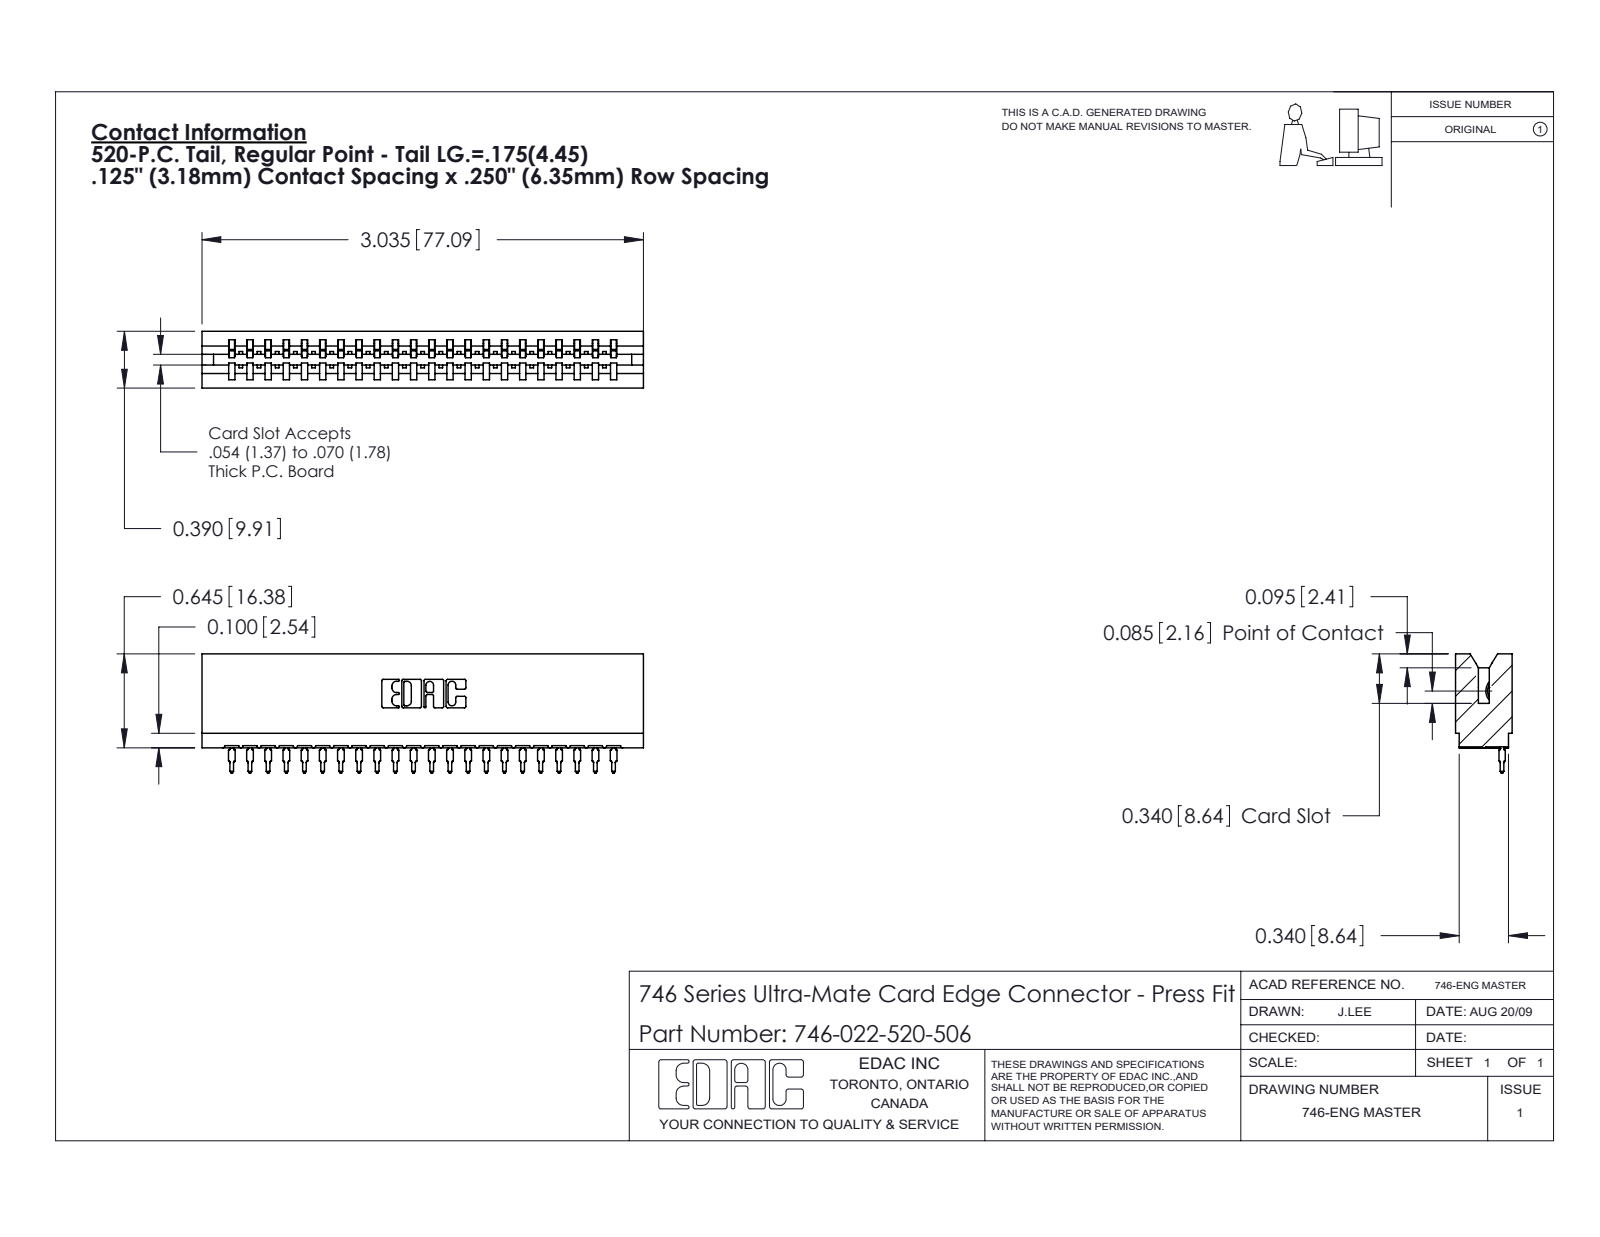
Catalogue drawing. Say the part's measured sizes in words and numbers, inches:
The part is named "746-022-520-506; 746 Part_.340 Slot Depth - 06; 746-292-001_520". Its 3-D file was written by "SolidWorks 2020 (CONFIG_CONTROL_DESIGN)". It is 23 solids with 2474 faces: 1442 planar, 460 cylindrical and 572 other. Overall it measures 3.035 by 0.819 by 0.39 inches. Its volume is 0.532 cubic inches and its surface area 17.52 square inches. Partial cylindrical surfaces (rounded edges, fillets, slot ends): 44 of radius 0.021, 23 of radius 0.015, 22 of radius 0.01, 6 of radius 0.007, 6 of radius 0.031, 4 of radius 0.005, 4 of radius 0.011, 3 of radius 0.026. The main face-to-face distances are 0.25, 0.057, 0.333, 0.39, 0.5, 0.042, 0.125, 0.025, 0.307, 0.292.
